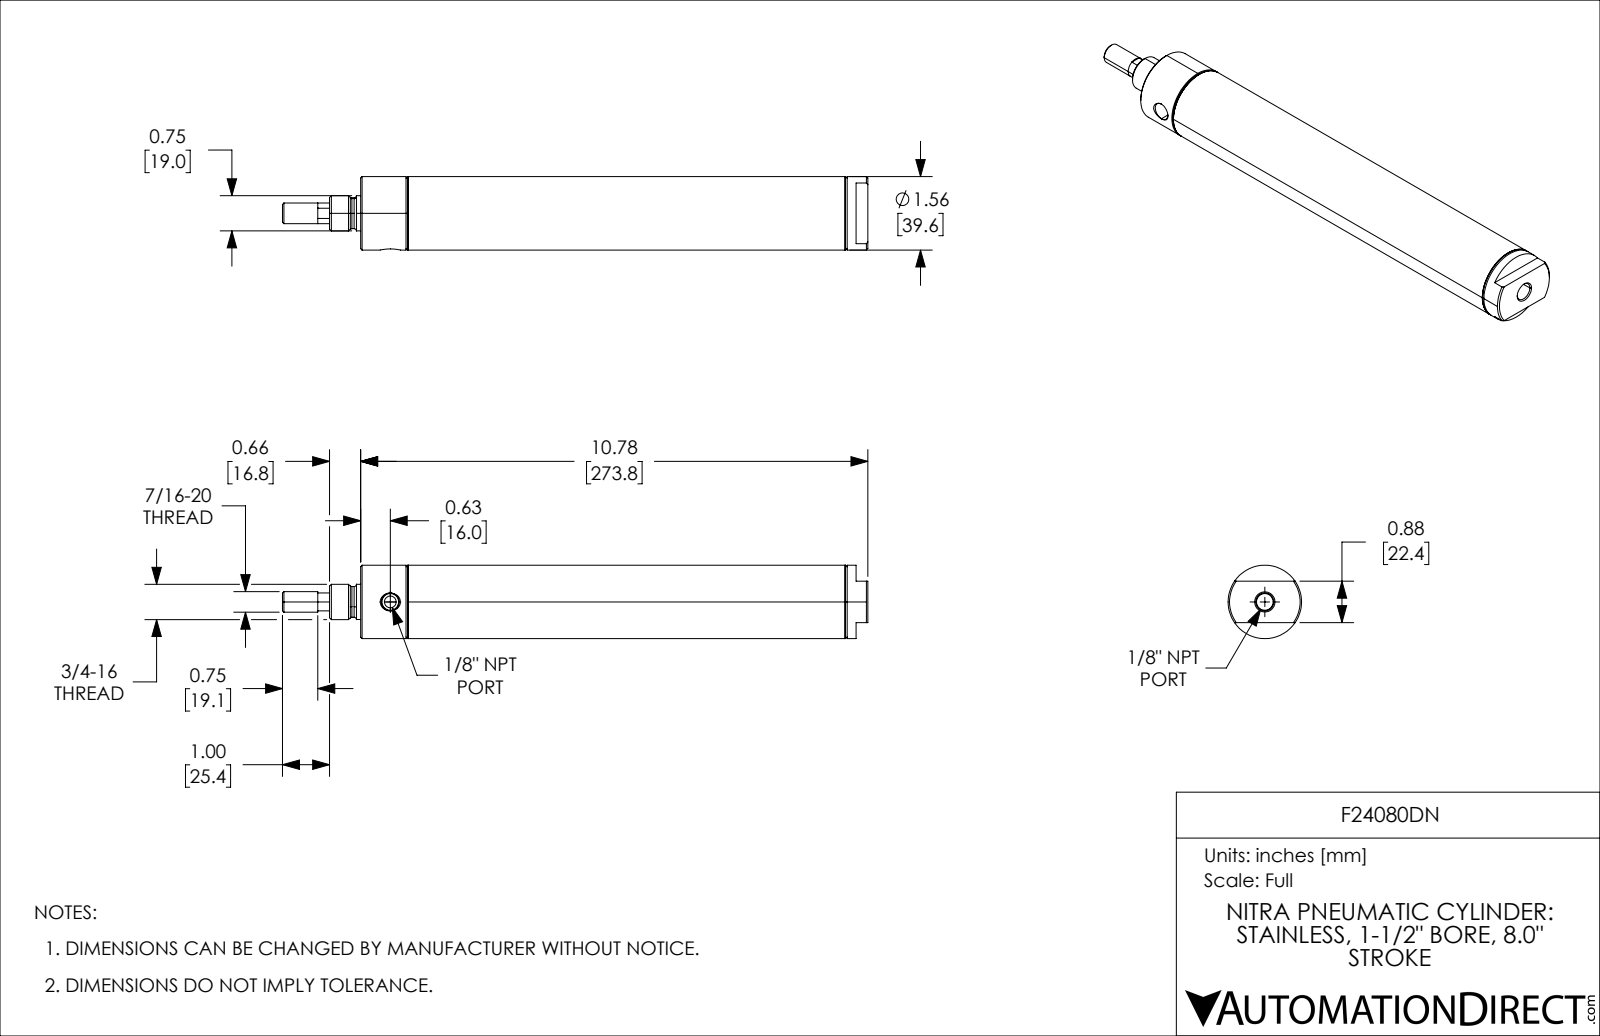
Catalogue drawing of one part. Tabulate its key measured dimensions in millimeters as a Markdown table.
| quantity | value |
| --- | --- |
| part name | F24080DN_7; F24080DN_5; F24080DN_9; F24080DN (+1 more) |
| STEP written by | SolidWorks 2021 (CONFIG_CONTROL_DESIGN) |
| units | millimeters |
| bodies | 4 solids, 126 faces (28 planar, 42 cylindrical, 56 other) |
| overall size | 315.93 × 39.62 × 39.62 |
| volume | 121 079 mm³ |
| surface area | 88 395 mm² |
| round holes (diameter × count) | 6.35 × 1, 11.73 × 1, 24.71 × 1, 36.36 × 1 |
| round bosses / shafts (diameter × count) | 39.62 × 1, 38.39 × 1, 19.05 × 1, 18.99 × 1, 16.6 × 1, 11.13 × 1, 11.11 × 1 |
| main face-to-face distances | 22.22, 6.35, 11.13, 203.2, 225.42, 30.86, 234.06, 256.28, 273.76, 242.9 |
